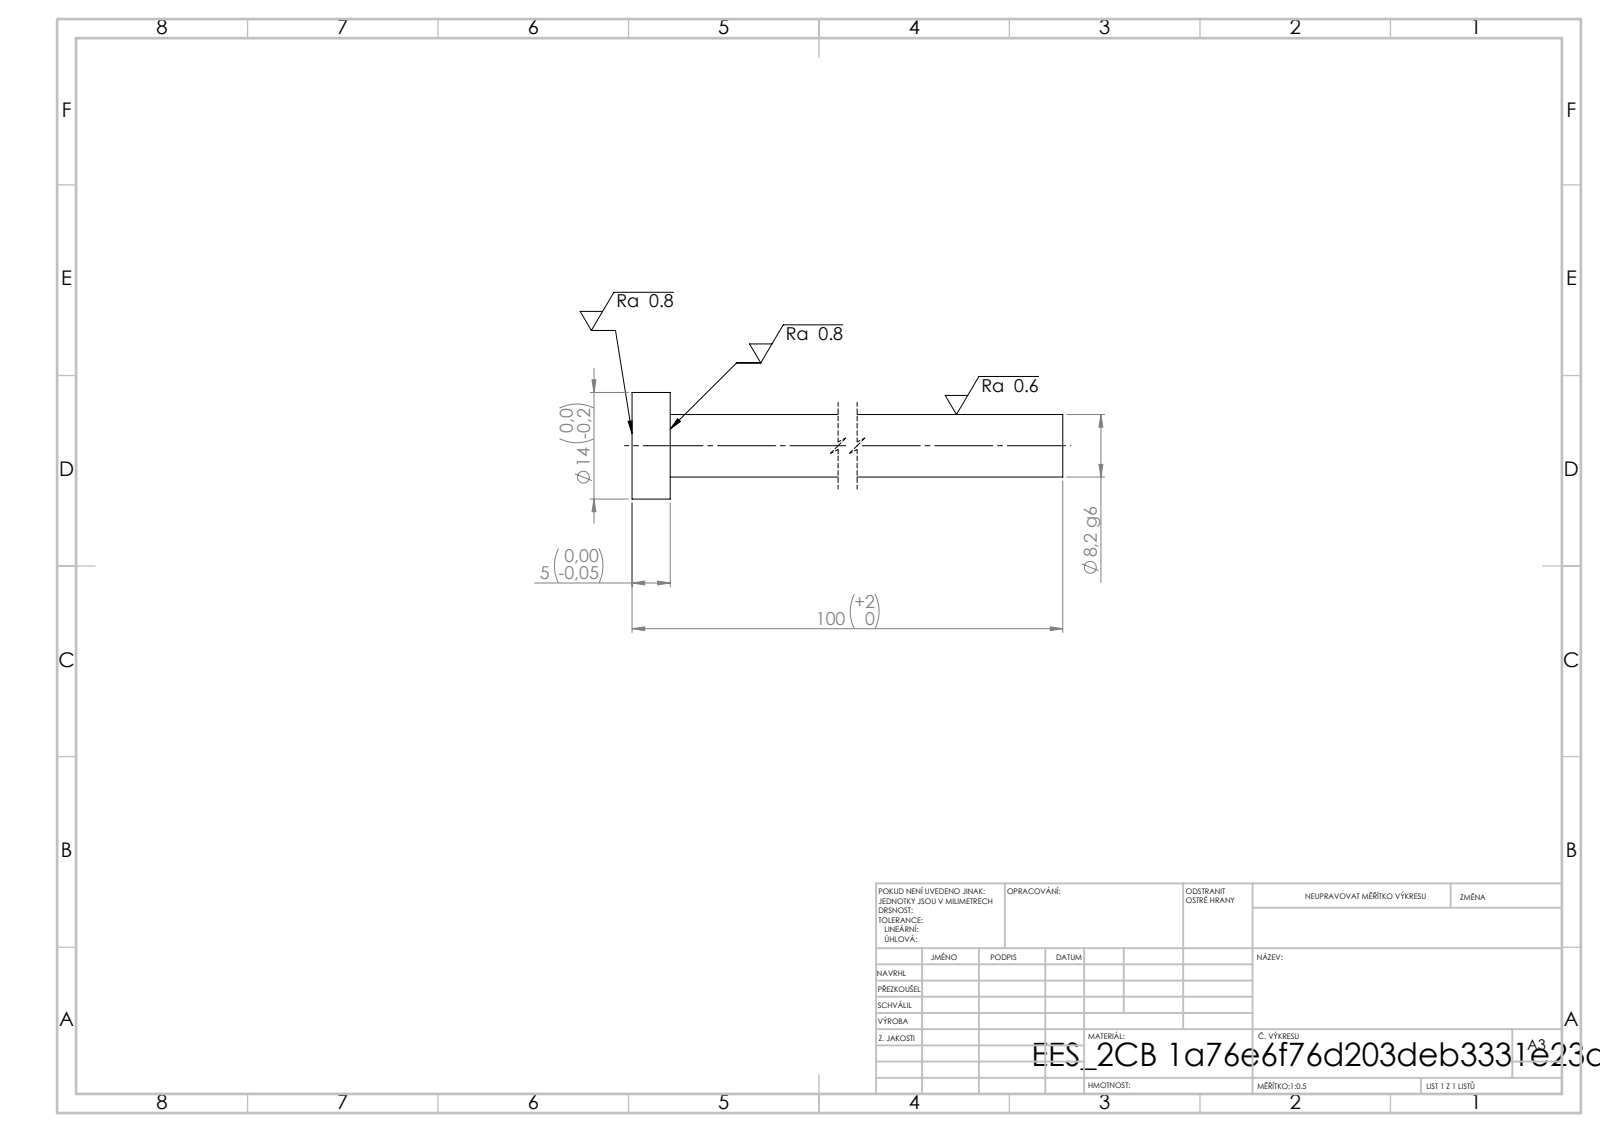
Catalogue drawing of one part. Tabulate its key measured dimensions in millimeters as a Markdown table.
| quantity | value |
| --- | --- |
| STEP written by | SolidWorks 2019 (CONFIG_CONTROL_DESIGN) |
| units | millimeters |
| bodies | 1 solid, 7 faces (3 planar, 4 cylindrical, 0 other) |
| overall size | 100 × 14 × 14 |
| volume | 5 787 mm³ |
| surface area | 2 975 mm² |
| round bosses / shafts (diameter × count) | 14 × 1, 8.2 × 1 |
| main face-to-face distances | 5, 100, 95 |
